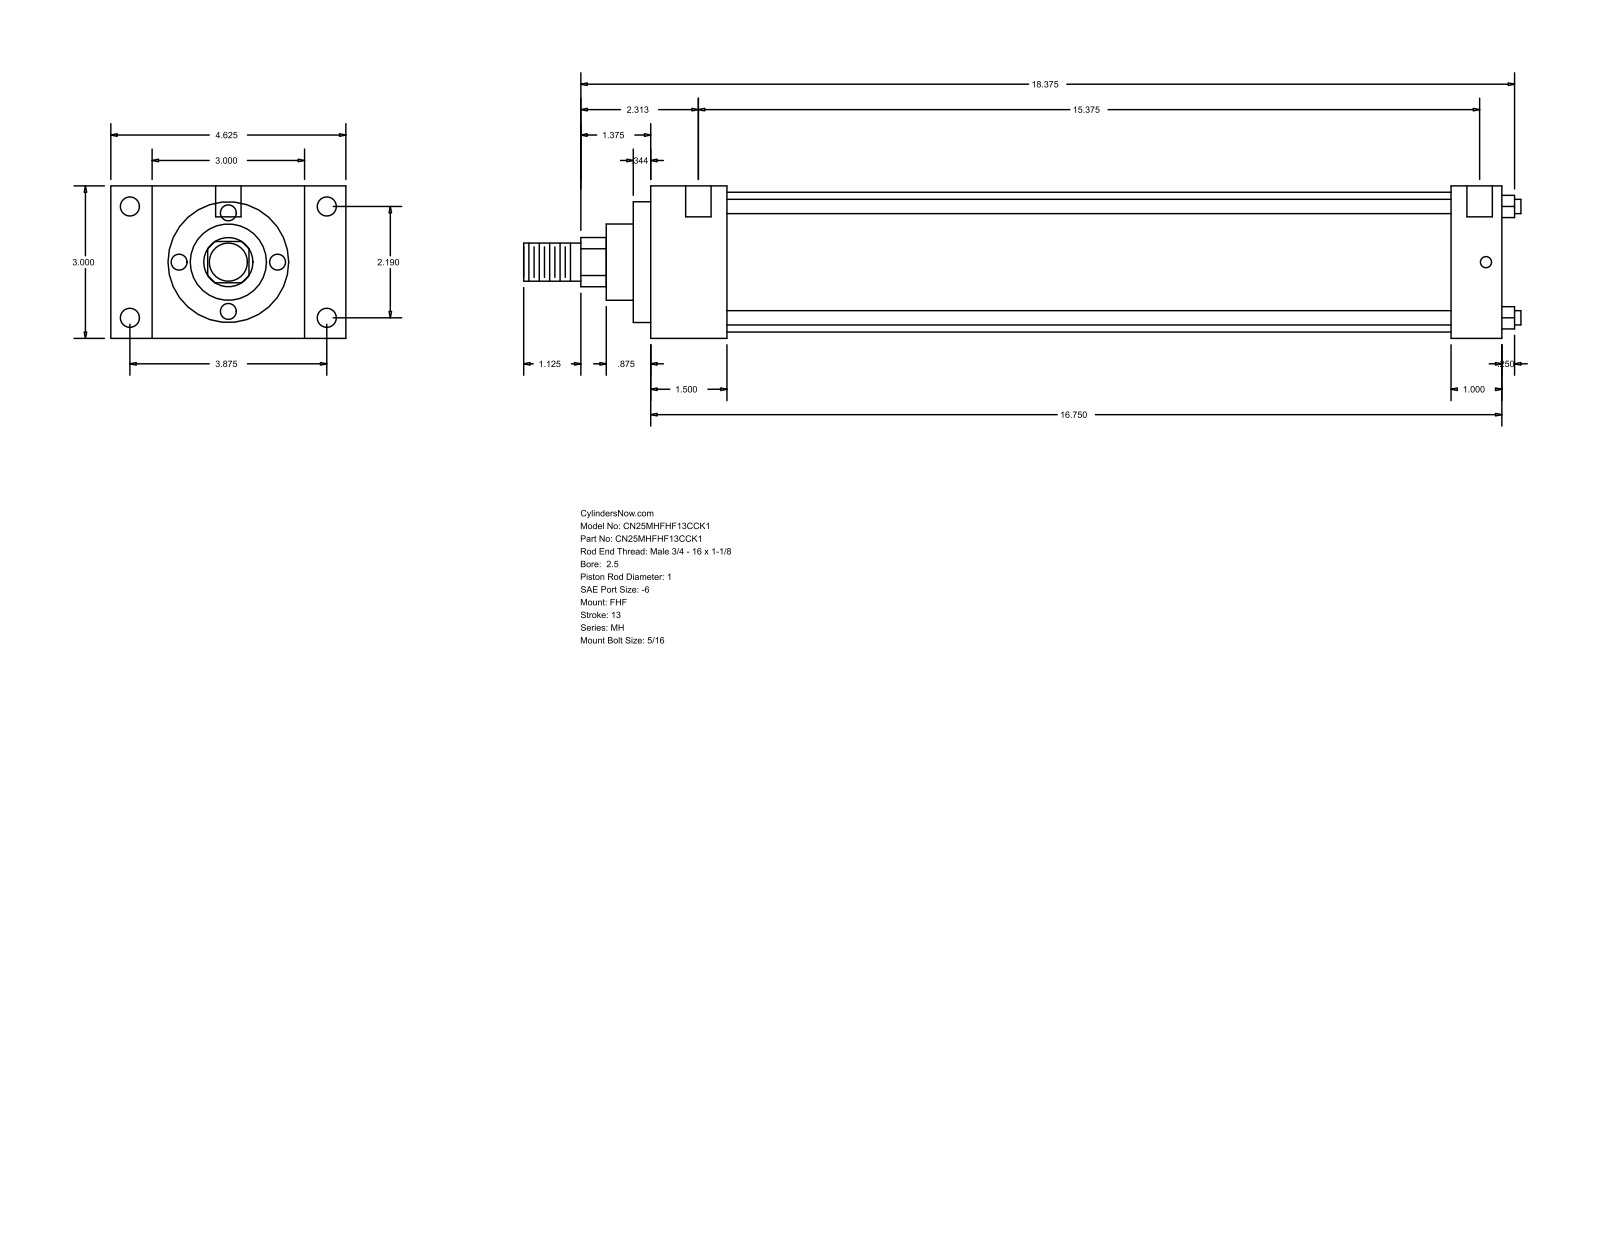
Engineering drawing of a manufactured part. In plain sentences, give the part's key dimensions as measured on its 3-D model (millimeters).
The part is named "MH_FHF__0250_1". Its 3-D file was written by "GSSL Pune (CONFIG_CONTROL_DESIGN)". It is 0 solids with 90 faces: 61 planar, 29 cylindrical and 0 other. Overall it measures 498.48 by 117.47 by 76.2 millimeters. Round holes: 4 of diameter 5.56, 4 of diameter 9.53, 2 of diameter 12.7. Round bosses or shafts: 4 of diameter 7.14, 1 of diameter 69.85, 1 of diameter 60.33, 1 of diameter 38.1, 1 of diameter 25.4, 1 of diameter 19.05. Partial cylindrical surfaces (rounded edges, fillets, slot ends): 1 of radius 12.29. The main face-to-face distances are 76.2, 425.46, 38.11, 387.35, 20.64, 96.84, 117.48, 400.06, 361.95, 25.4. The hole center spacings are 55.62, 98.42, 113.05, 398.46, 3.18, 4.76, 390.52, 393.7.
